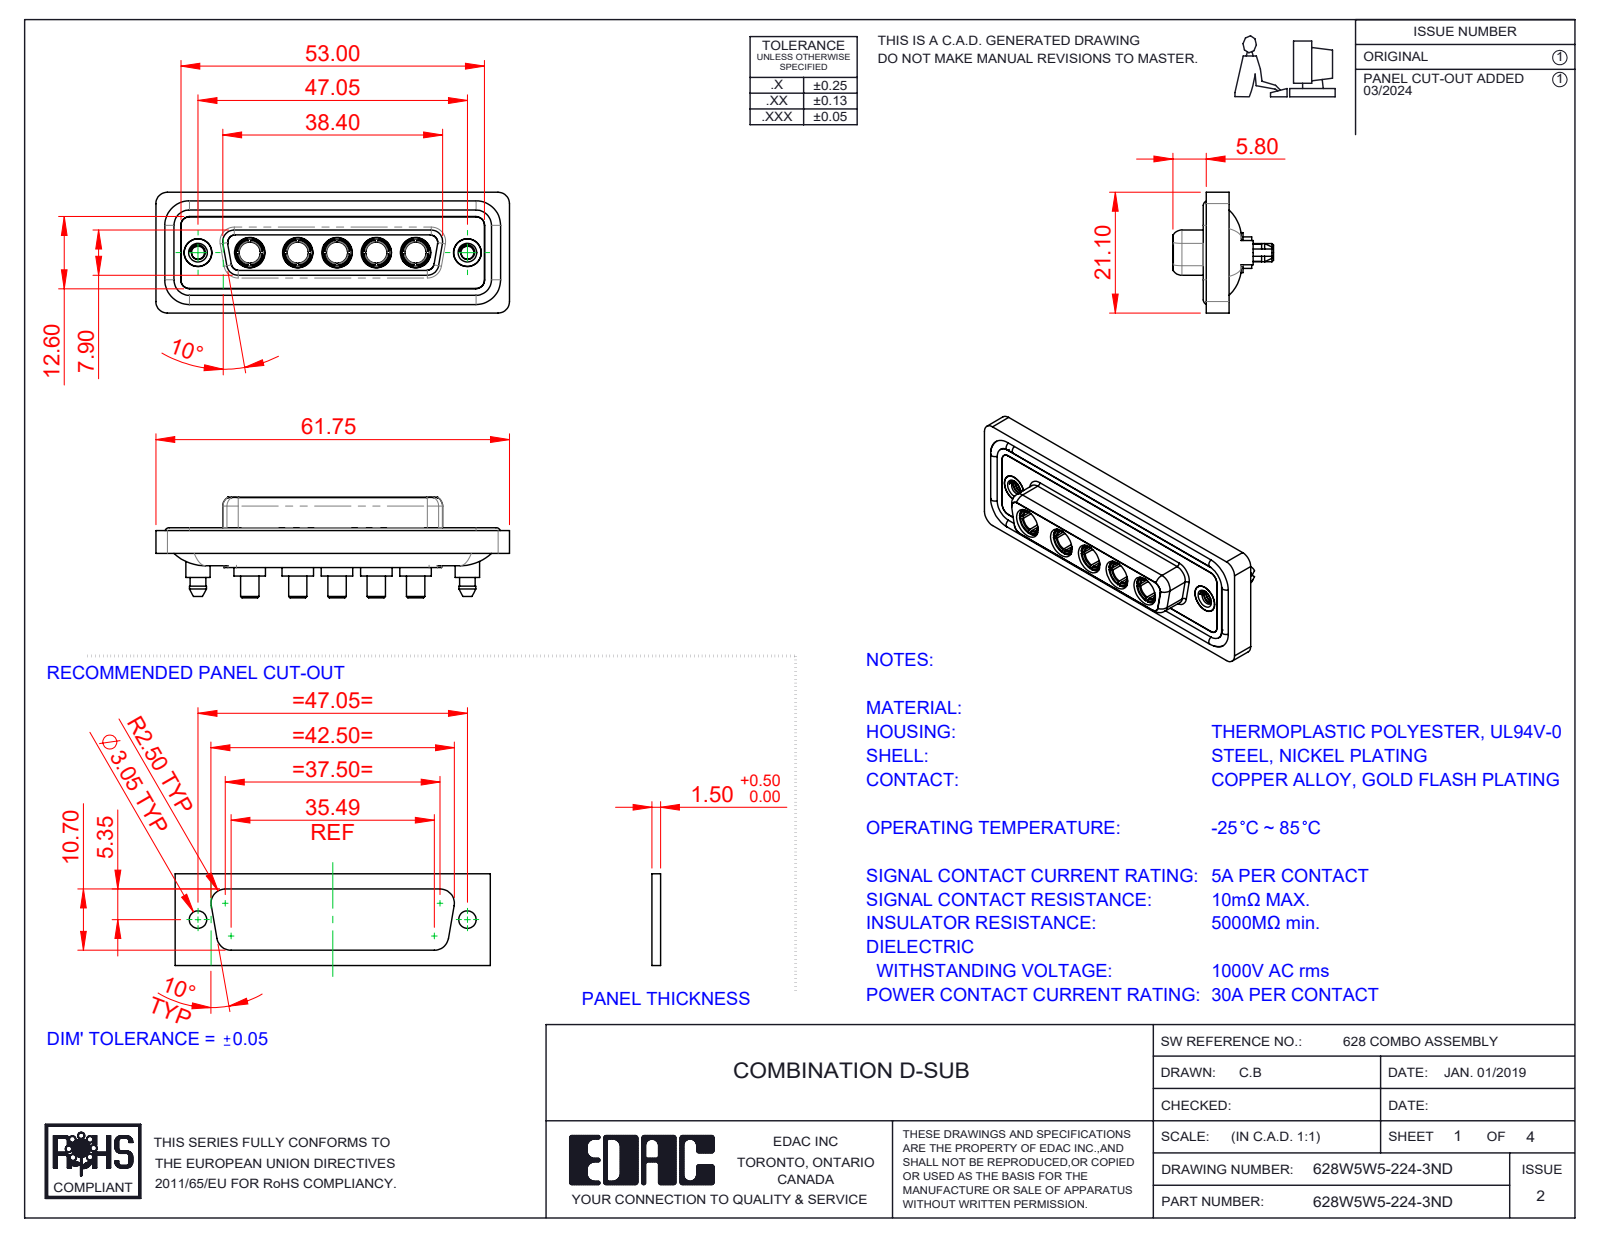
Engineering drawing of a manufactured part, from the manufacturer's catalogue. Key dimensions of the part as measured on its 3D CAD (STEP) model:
Part name (STEP PRODUCT): 628Combo Housing_5W5; 628Combo Shell Front_25 Contacts; 628W5W5-224-3ND; Power Socket_30A S (+3 more)
STEP written by: SolidWorks 2023 (CONFIG_CONTROL_DESIGN)
Units: millimetres
Bodies: 17 solids, 822 faces (266 planar, 351 cylindrical, 205 other)
Overall size (bounding box): 61.75 × 21.1 × 17.55
Volume: 8 343 mm³ · Surface area: 13 778 mm²
Round holes (diameter × count): ⌀4.85 ×7, ⌀3.7 ×5, ⌀5.3 ×5, ⌀2.26 ×2, ⌀4 ×2, ⌀4.05 ×2, ⌀5 ×2
Round bosses / shafts (diameter × count): ⌀5.5 ×5, ⌀5.2 ×5, ⌀4.96 ×5, ⌀4.75 ×5, ⌀3.75 ×5, ⌀3.2 ×5, ⌀1.6 ×4, ⌀5.4 ×2
Partial cylindrical surfaces — rounded edges, fillets, slot ends (radius × count): R1.5 ×24, R2 ×18, R1.6 ×10, R1.35 ×8, R2.1 ×5, R0.25 ×4, R0.5 ×4, R0.6 ×4
Main face-to-face distances: 0.4, 1.8, 7.45, 5.65, 0.5, 7.05, 6.6, 1.6, 1.1, 2.9
Hole centre spacings: 6.86, 9.04, 13.72, 38.01, 8.39, 15.25, 15.9, 17.43
